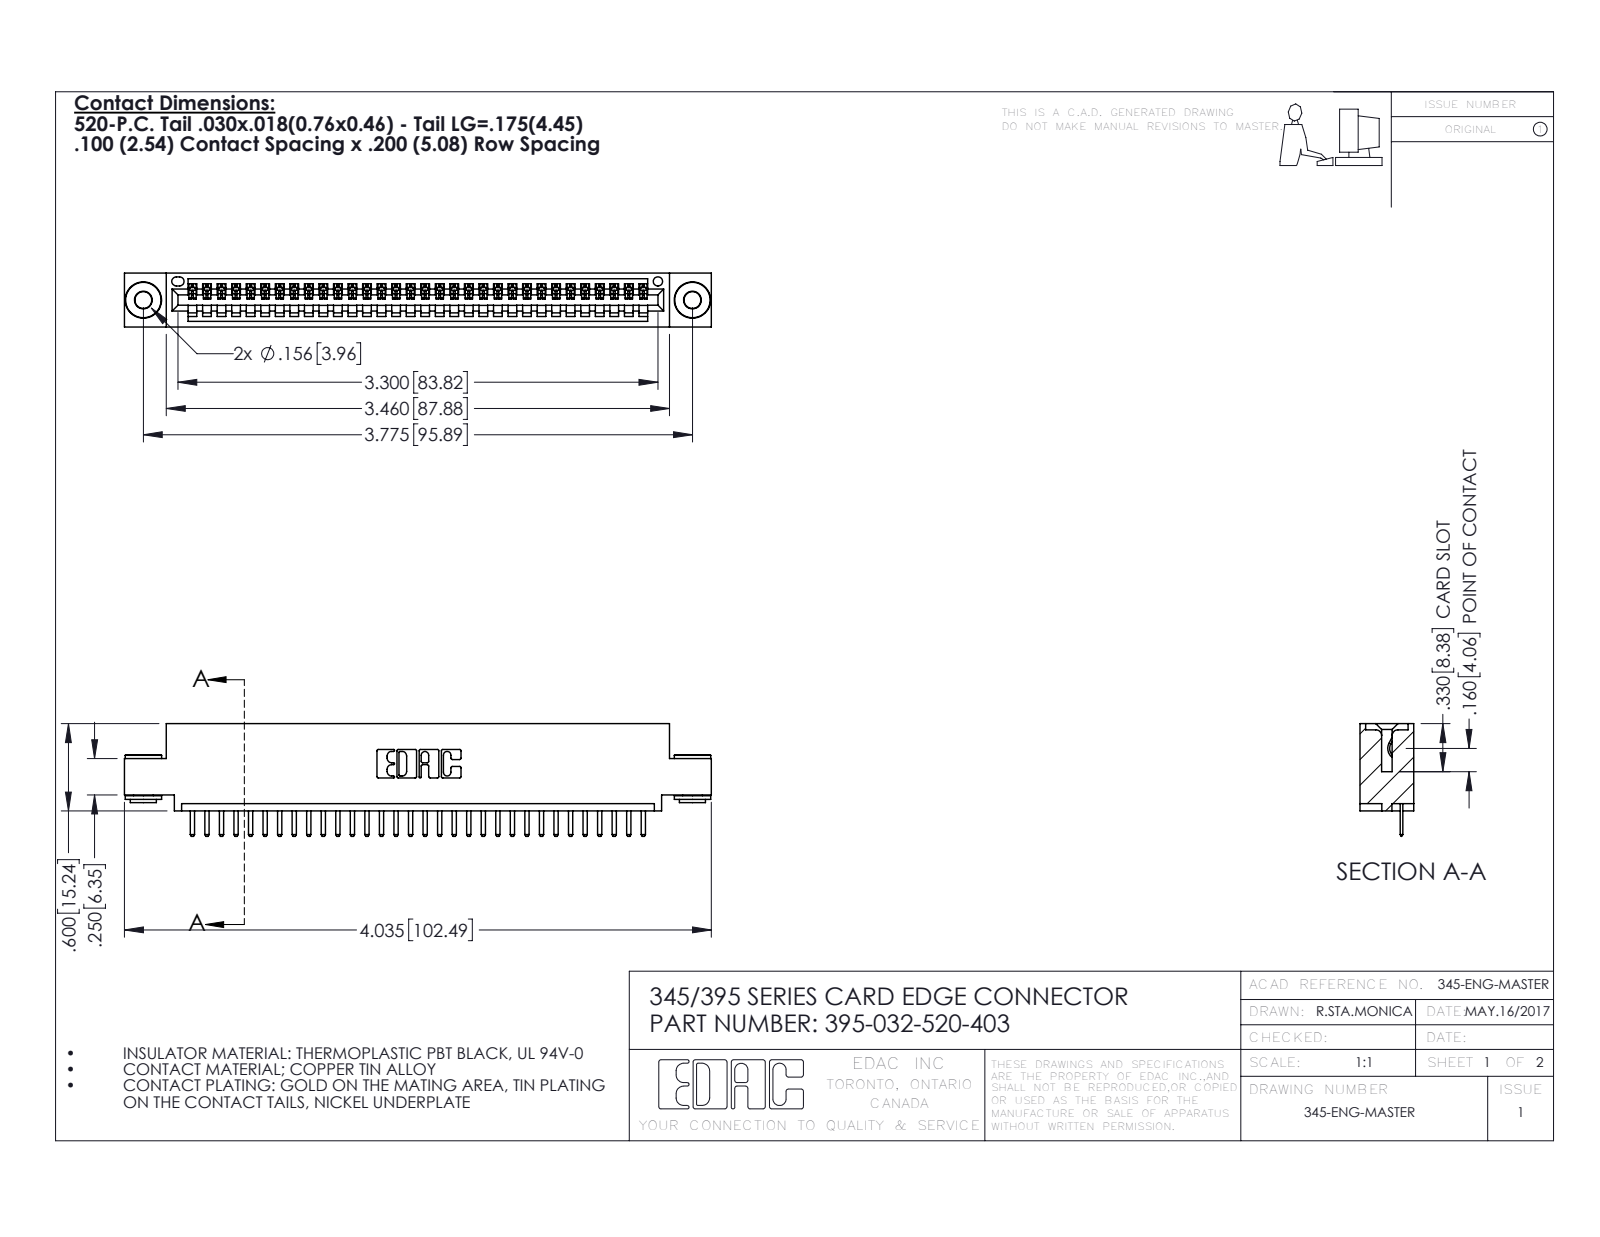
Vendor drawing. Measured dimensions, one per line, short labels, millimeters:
name: 345 Part_0.110 Offset - 0.156 Dia-TH; 345-292-001_345-293-120; 395-032-520-403; 345-250-002_345-250-002-102
written by: SolidWorks 2016 (CONFIG_CONTROL_DESIGN)
unit: mm
bodies: 35 solids, 2152 faces (1438 planar, 706 cylindrical, 8 other)
size: 102.5 × 19.7 × 9.4
volume: 9 500 mm³; area: 12 490 mm²
holes: 2× ⌀2.9, 2× ⌀4, 1× ⌀1.6
bosses: 2× ⌀6.4, 2× ⌀4.6, 2× ⌀3.5
rounds: 66× R0.3, 64× R0.2, 22× R0.3, 6× R0.2, 6× R0.8, 3× R0.7, 2× R0.8, 2× R1
face distances: 1.8, 7.6, 9.4, 5.1, 0.6, 2.5, 6.9, 5.7, 1.8, 3.8
hole spacings: 6.9, 89.9, 95.9
